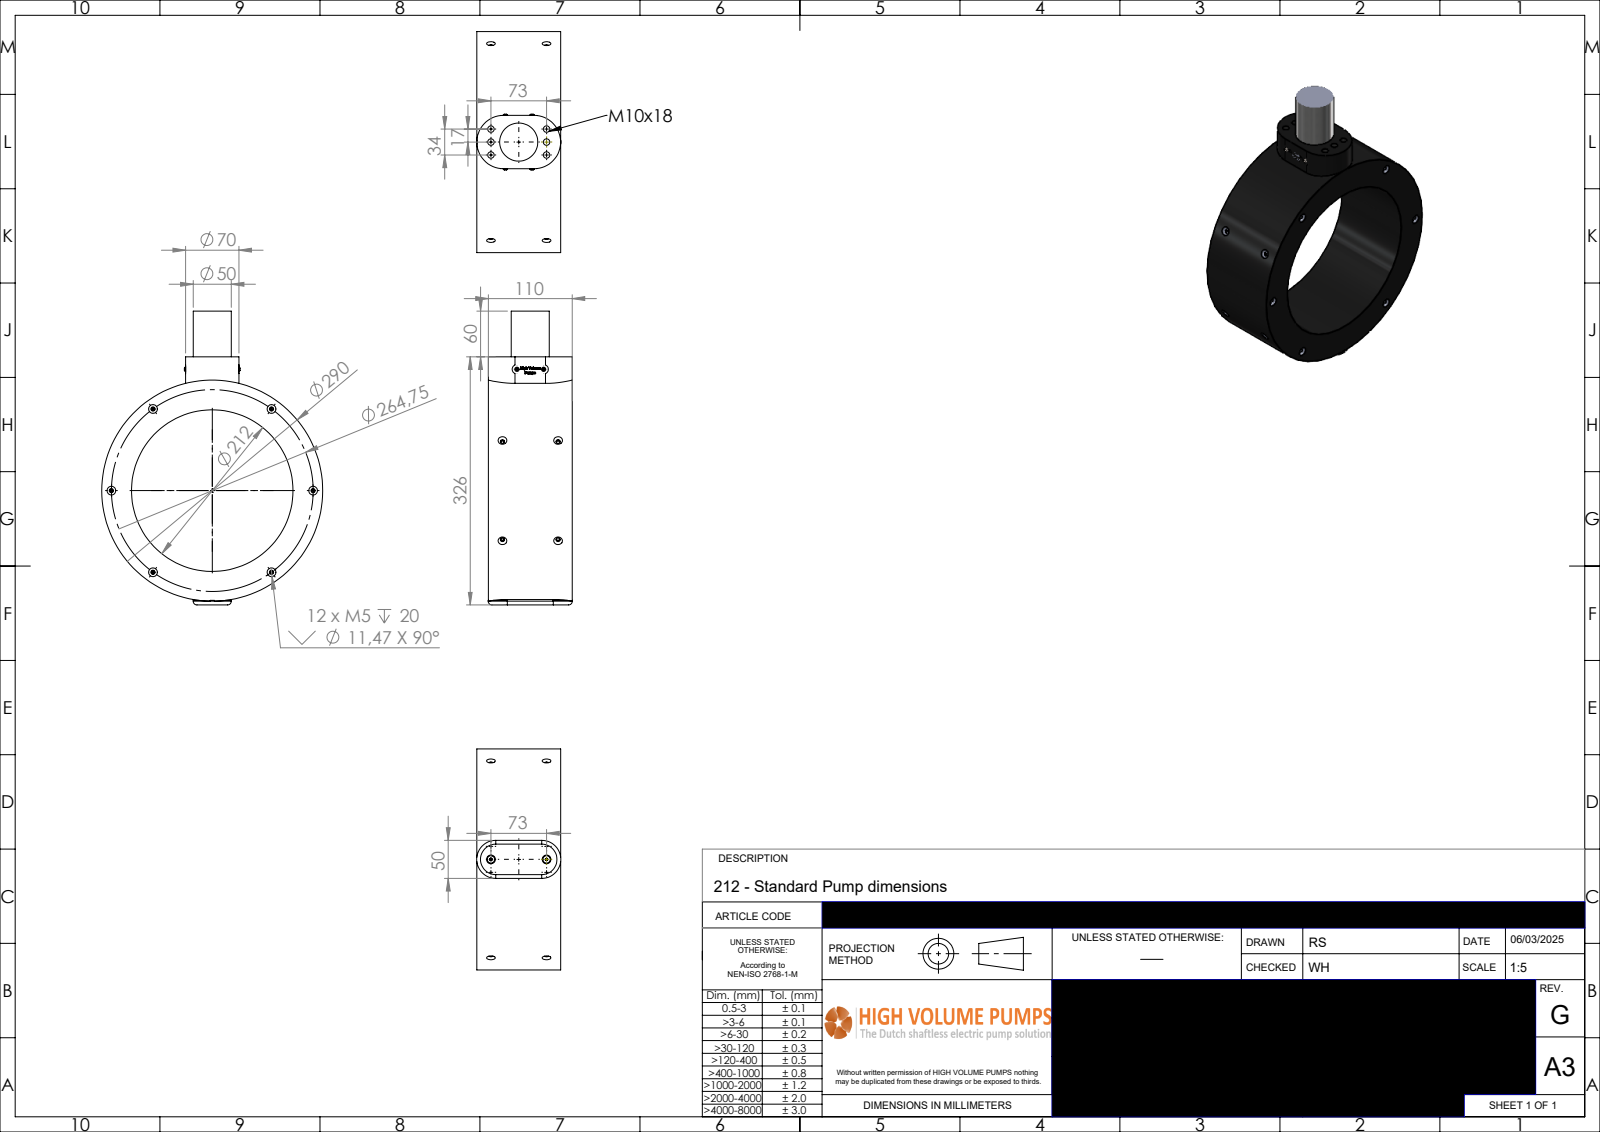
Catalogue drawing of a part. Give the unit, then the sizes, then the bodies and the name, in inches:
Units: inches
Overall size (bounding box): 15.175 × 11.417 × 4.345
Round holes (diameter × count): ⌀0.165 ×10, ⌀0.217 ×10, ⌀0.335 ×6, ⌀8.346 ×1
Round bosses / shafts (diameter × count): ⌀0.38 ×2, ⌀0.224 ×2, ⌀11.417 ×1, ⌀1.969 ×1
Partial cylindrical surfaces — rounded edges, fillets, slot ends (radius × count): R0.984 ×4, R0.197 ×2, R0.246 ×2, R1.378 ×2
Main face-to-face distances: 4.333, 12.813, 2.362, 15.175, 2.756, 12.008, 0.805, 3.167, 0.394, 1.969
Hole centre spacings: 2.874, 0.669, 2.951, 4.732, 5.211, 9.287, 1.339, 3.17
Volume: 227.2 in³ · Surface area: 410.2 in²
Bodies: 1 solid, 694 faces (353 planar, 69 cylindrical, 272 other)
Part name (STEP PRODUCT): P-212-030-rev-G-SP
STEP written by: SolidWorks 2024 (AUTOMOTIVE_DESIGN)
